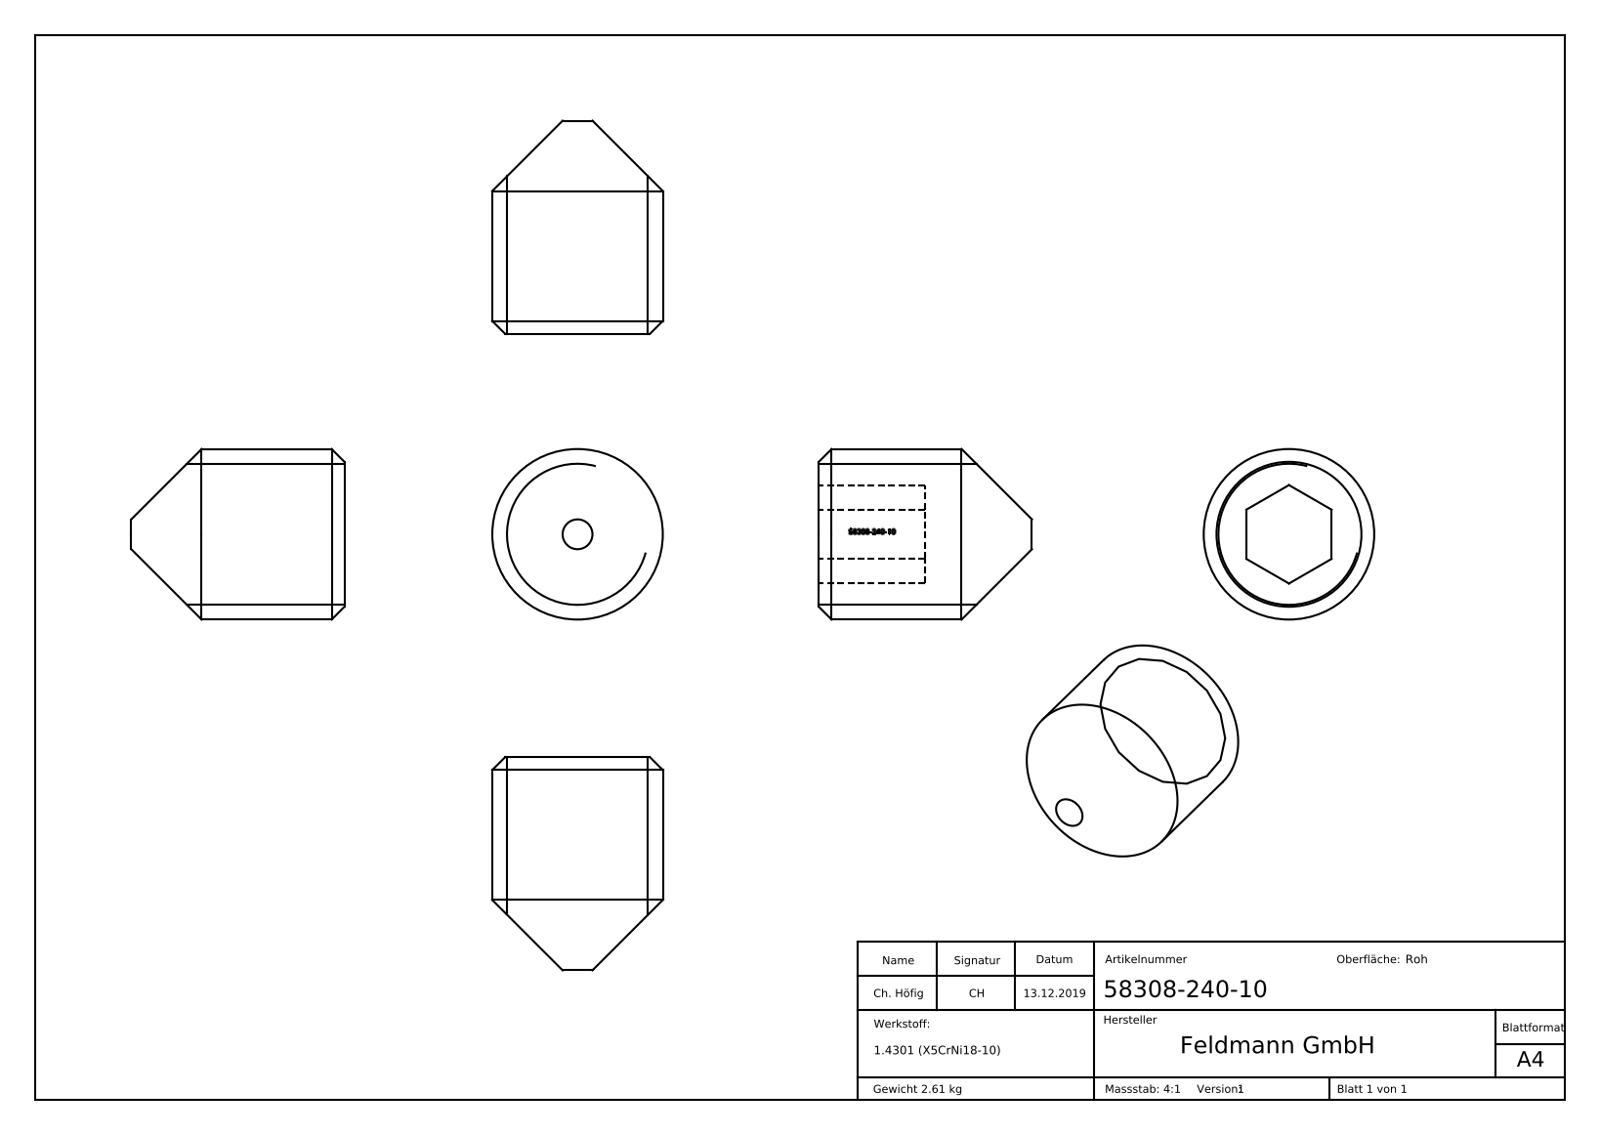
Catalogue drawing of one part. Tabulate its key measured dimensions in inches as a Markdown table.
| quantity | value |
| --- | --- |
| part name | 58308-240-10 |
| STEP written by | SolidWorks 2015 (CONFIG_CONTROL_DESIGN) |
| units | inches |
| bodies | 1 solid, 169 faces (70 planar, 1 cylindrical, 98 other) |
| overall size | 2.756 × 0.315 × 0.315 |
| volume | 0.02 in³ |
| surface area | 0.543 in² |
| round bosses / shafts (diameter × count) | 0.315 × 1 |
| main face-to-face distances | 0.157, 0.197, 0.394, 0.161, 0.018, 0.262, 0.065, 0.131, 0.019, 0.067 |
